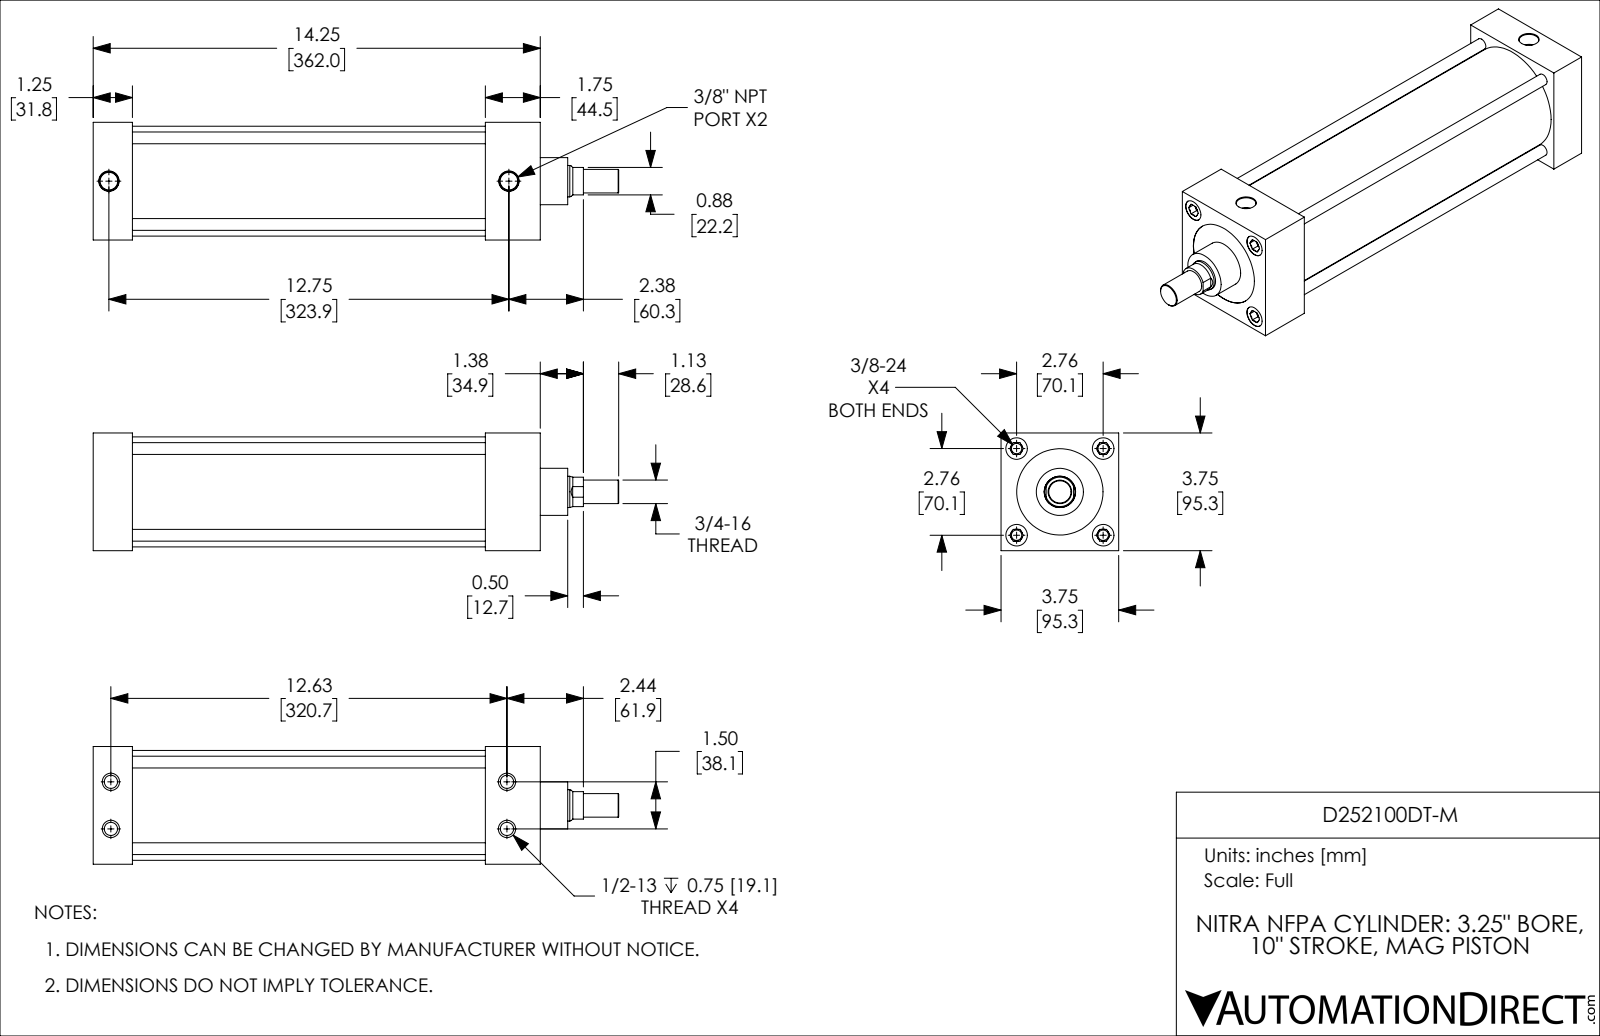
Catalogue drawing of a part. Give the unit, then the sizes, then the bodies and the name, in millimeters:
Units: millimetres
Overall size (bounding box): 425.5 × 95.3 × 95.3
Round holes (diameter × count): ⌀8.4 ×4, ⌀10.7 ×4, ⌀17.4 ×4, ⌀14.3 ×2, ⌀25.4 ×1, ⌀69.9 ×1, ⌀82.6 ×1
Round bosses / shafts (diameter × count): ⌀9.5 ×4, ⌀88.9 ×1, ⌀82.5 ×1, ⌀38.1 ×1, ⌀25.4 ×1, ⌀19.1 ×1
Partial cylindrical surfaces — rounded edges, fillets, slot ends (radius × count): R11.9 ×1
Main face-to-face distances: 31.8, 95.3, 317.5, 285.8, 63.5, 254, 362, 330.2, 298.5, 44.5
Hole centre spacings: 19.1, 49.6, 70.1, 322.8, 38.1, 99.1, 320.7, 322.9
Volume: 1 319 000 mm³ · Surface area: 317 400 mm²
Bodies: 2 solids, 198 faces (58 planar, 62 cylindrical, 78 other)
Part name (STEP PRODUCT): D252100DT-M_BODY; D252100DT-M; D252100DT-M_PISTON_KK1
STEP written by: SolidWorks 2019 (CONFIG_CONTROL_DESIGN)
